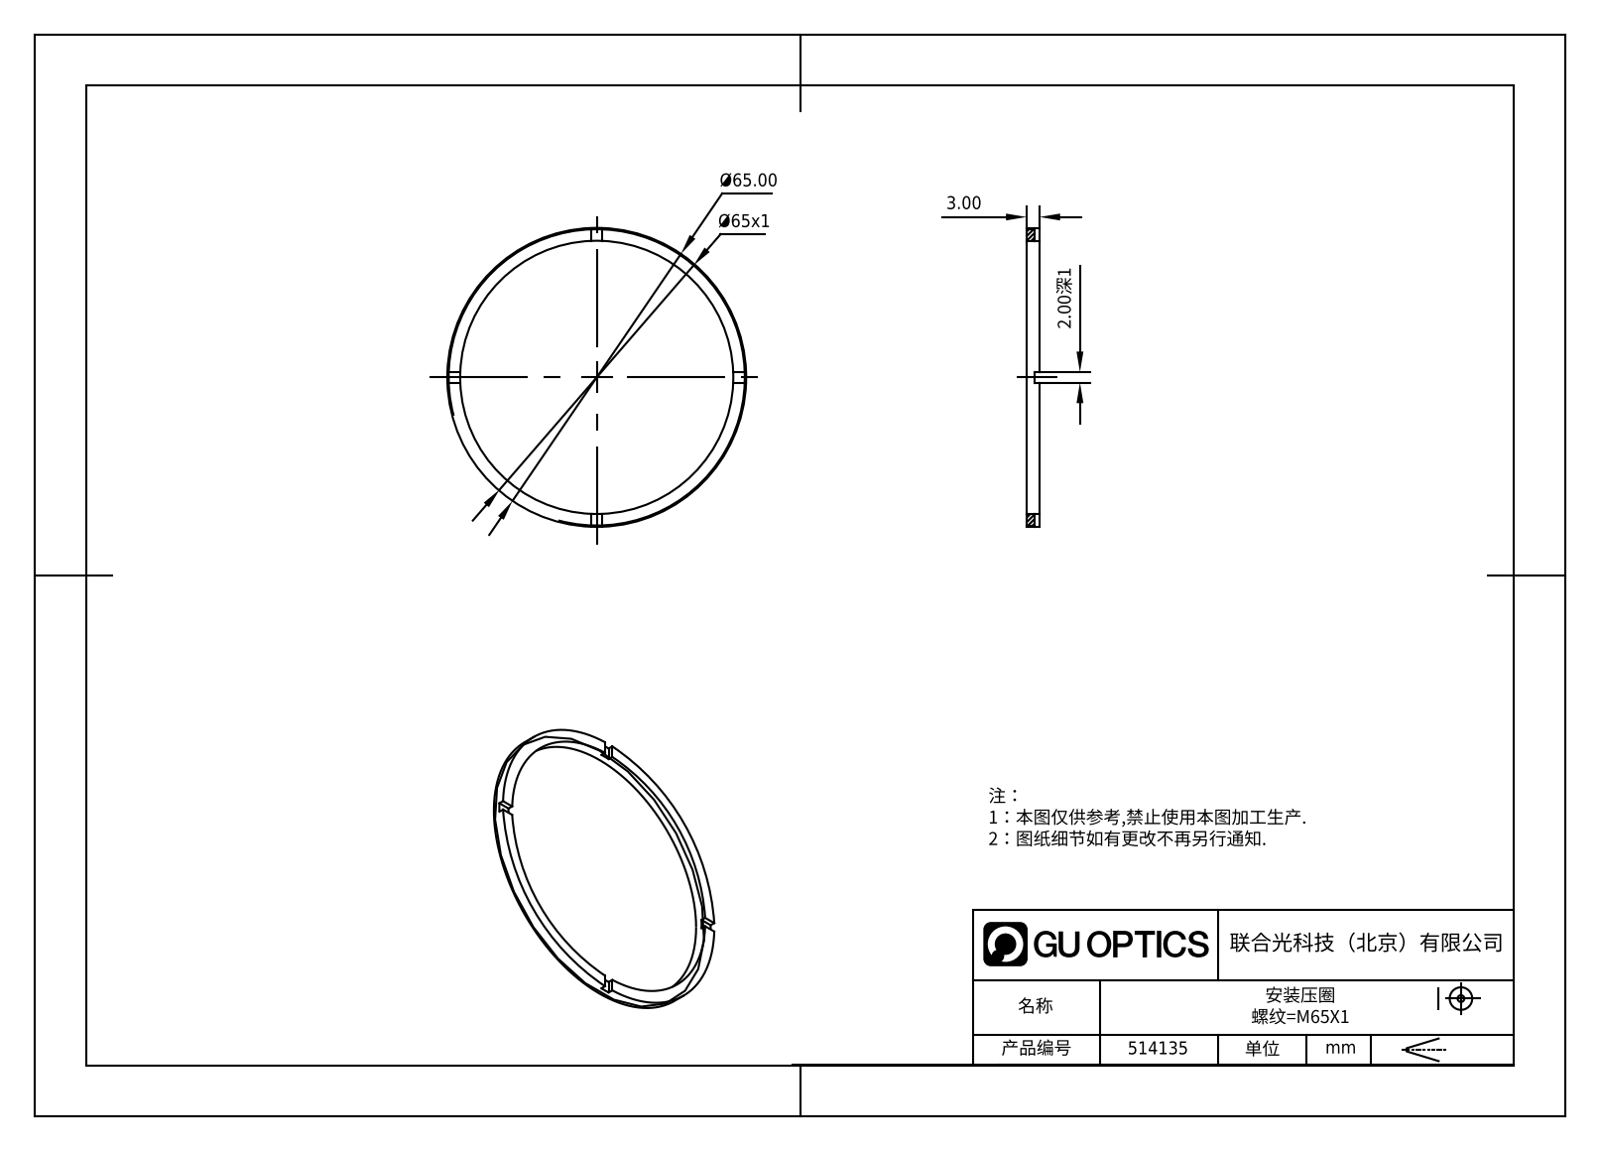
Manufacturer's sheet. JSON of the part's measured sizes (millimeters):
{"part_name": "514135", "step_written_by": "SolidWorks 2020 (CONFIG_CONTROL_DESIGN)", "units": "millimeters", "bodies": {"solids": 1, "faces": 21, "planar": 17, "cylindrical": 4, "other": 0}, "overall_size": [65, 65, 3], "volume_mm3": 1453, "surface_area_mm2": 2164, "round_holes": [[60, 1]], "round_bosses_or_shafts": [[65, 1]], "face_to_face_distances": [3, 2, 1]}
